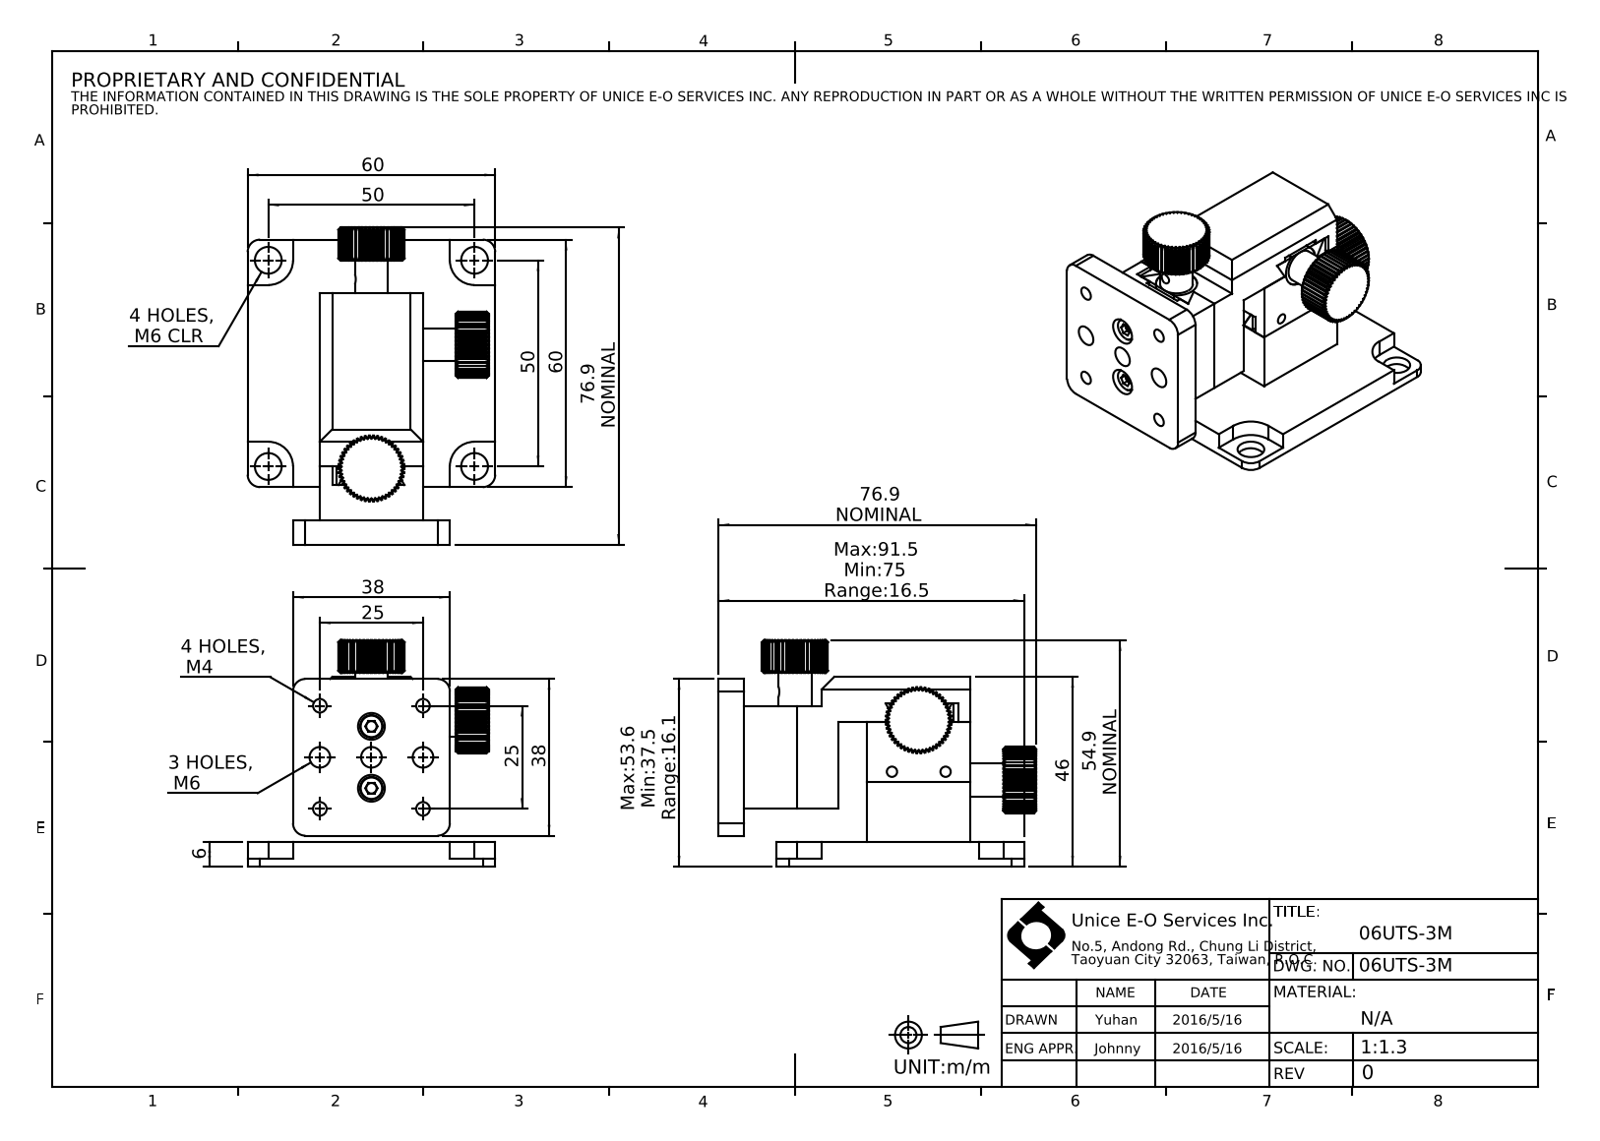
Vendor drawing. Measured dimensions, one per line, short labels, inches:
name: 06UTS-3M
written by: SolidWorks 2016 (CONFIG_CONTROL_DESIGN)
unit: in
bodies: 21 solids, 1191 faces (531 planar, 308 cylindrical, 352 other)
size: 3.028 × 2.362 × 2.161
volume: 4.271 in³; area: 56.58 in²
holes: 18× ⌀0.098, 8× ⌀0.256, 4× ⌀0.13, 4× ⌀0.134, 4× ⌀0.197, 3× ⌀0.126, 3× ⌀0.394
bosses: 4× ⌀0.217, 4× ⌀0.118, 3× ⌀0.315
rounds: 8× R0.118, 4× R0.236, 3× R0.315
face distances: 0.236, 0.984, 0.571, 0.256, 0.433, 1.299, 1.142, 0.748, 0.61, 0.217
hole spacings: 0.984, 0.492, 0.512, 0.53, 0.574, 0.696, 0.928, 1.1
